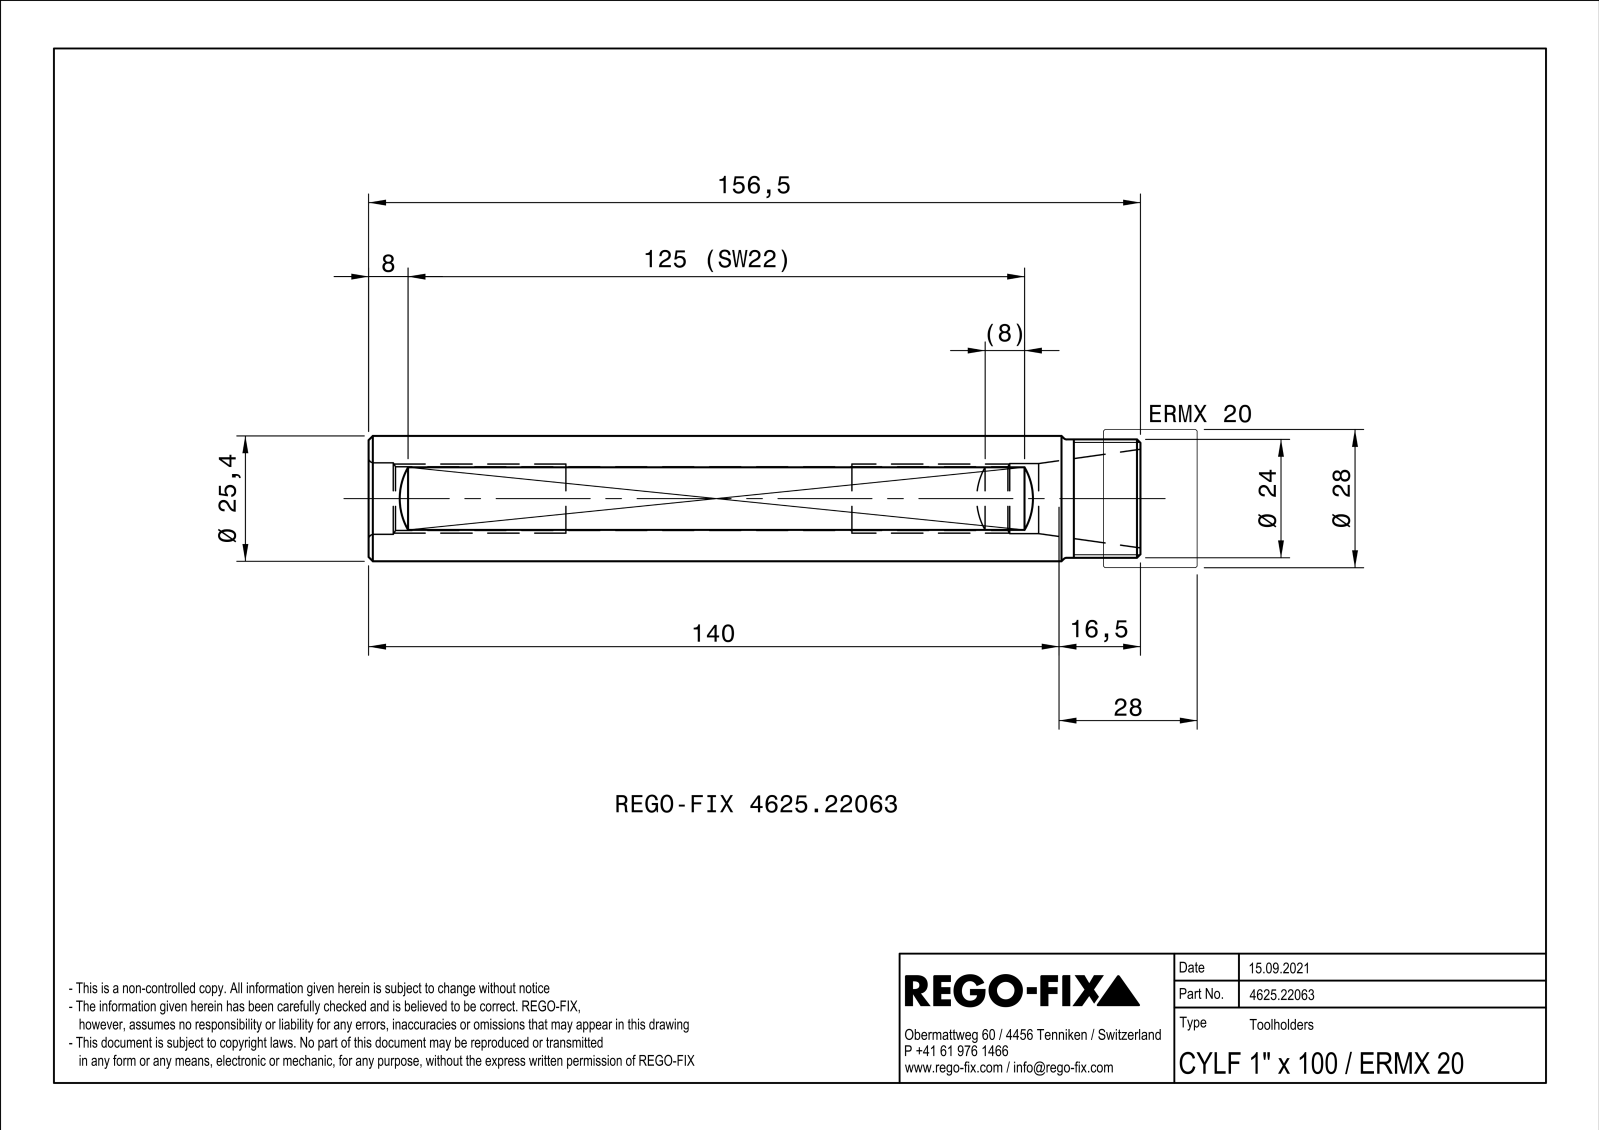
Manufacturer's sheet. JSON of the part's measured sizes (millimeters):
{"part_name": "NOCUT", "step_written_by": "SIEMENS PLM Software Solid Edge ST10 (AUTOMOTIVE_DESIGN)", "units": "millimeters", "bodies": {"solids": 1, "faces": 25, "planar": 8, "cylindrical": 8, "other": 9}, "overall_size": [116.5, 25.4, 25.4], "volume_mm3": 39038, "surface_area_mm2": 14693, "round_holes": [[12.92, 1], [14.2, 1], [14.5, 1]], "round_bosses_or_shafts": [[25.4, 1], [24, 1]], "face_to_face_distances": [22, 116.5, 44.54, 9.9]}
